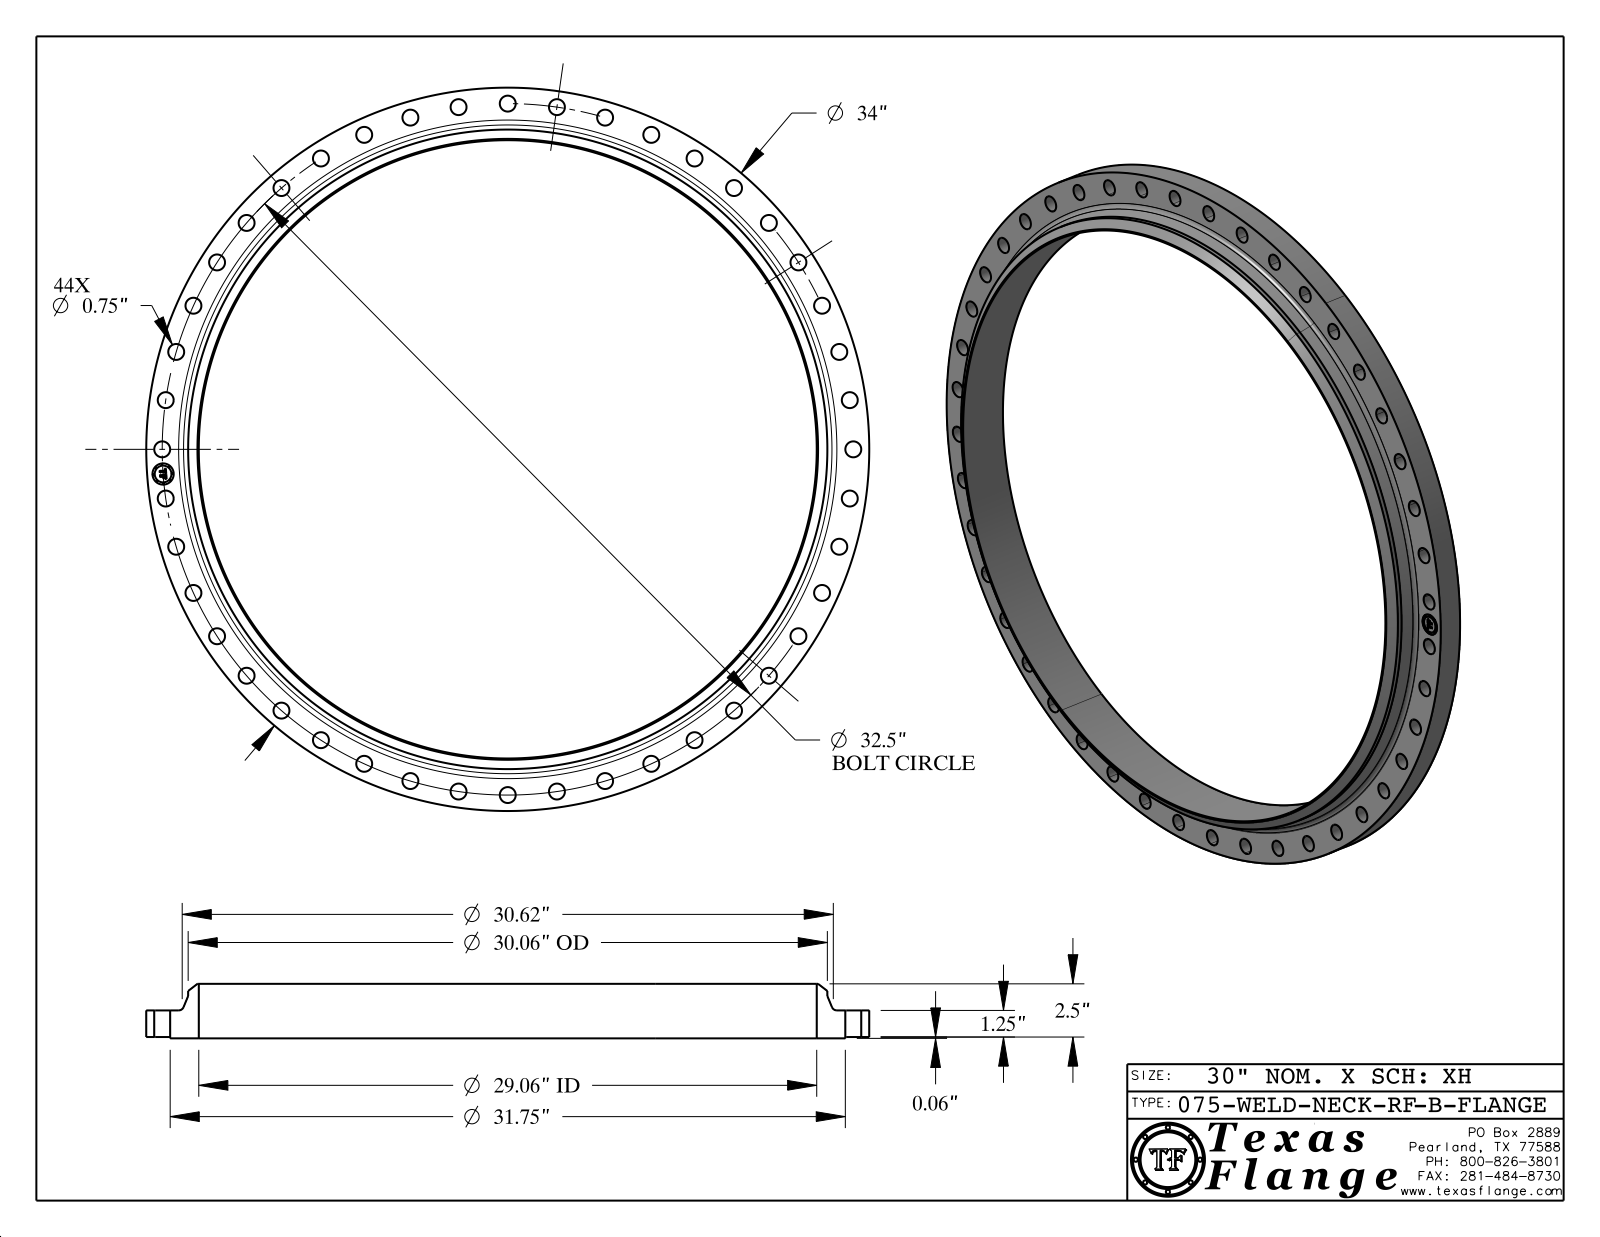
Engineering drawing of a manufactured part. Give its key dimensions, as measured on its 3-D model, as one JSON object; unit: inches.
{"part_name": "075-WELD-NECK-RF, Series B", "step_written_by": "CATIA V5 STEP AP214 (AUTOMOTIVE_DESIGN)", "units": "inches", "bodies": {"solids": 1, "faces": 491, "planar": 369, "cylindrical": 116, "other": 6}, "overall_size": [34, 34, 2.563], "volume_in3": 350.3, "surface_area_in2": 1026, "round_holes": [[0.75, 44], [1, 1], [29.06, 1]], "round_bosses_or_shafts": [[0.061, 8], [34, 1], [31.75, 1], [30.06, 1], [0.788, 1]], "face_to_face_distances": [1.313, 1.25, 0.063, 2.563, 2.5, 1.298, 1.235, 0.015, 1.265, 0.298], "hole_center_spacings": [16.25, 9.156, 32.417, 31.183, 32.169, 4.625, 26.018, 22.981]}
